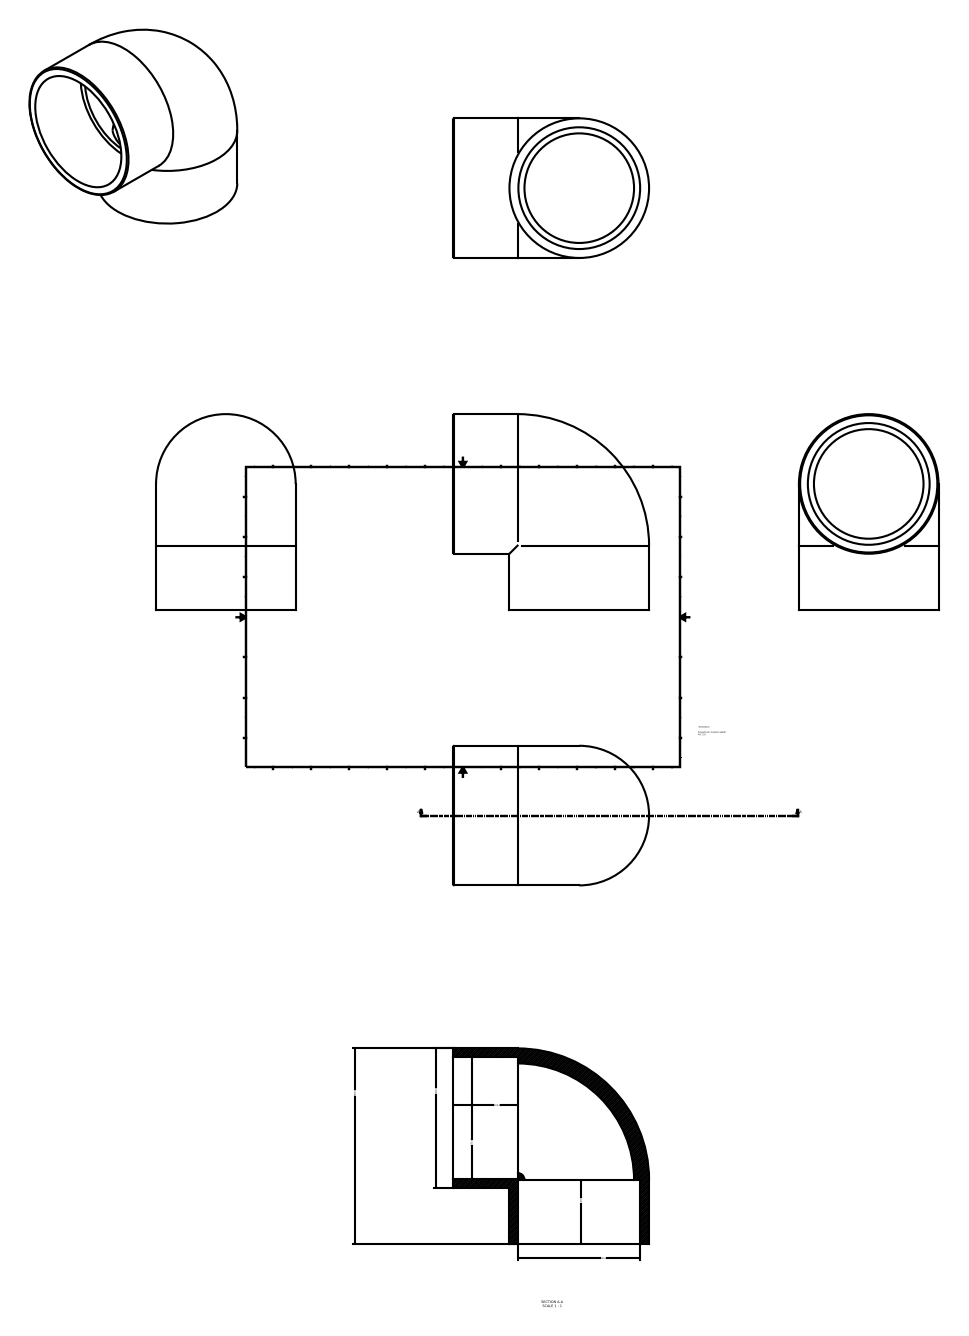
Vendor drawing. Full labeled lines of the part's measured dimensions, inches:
Part name (STEP PRODUCT): (_AS)050500225
STEP written by: Autodesk Inventor 2015 (AUTOMOTIVE_DESIGN)
Units: inches
Bodies: 1 solid, 11 faces (4 planar, 4 cylindrical, 3 other)
Overall size (bounding box): 14.252 × 14.252 × 10.157
Volume: 406.6 in³ · Surface area: 1 022 in²
Round holes (diameter × count): ⌀8.858 ×2
Round bosses / shafts (diameter × count): ⌀10.157 ×2
Main face-to-face distances: 4.685
